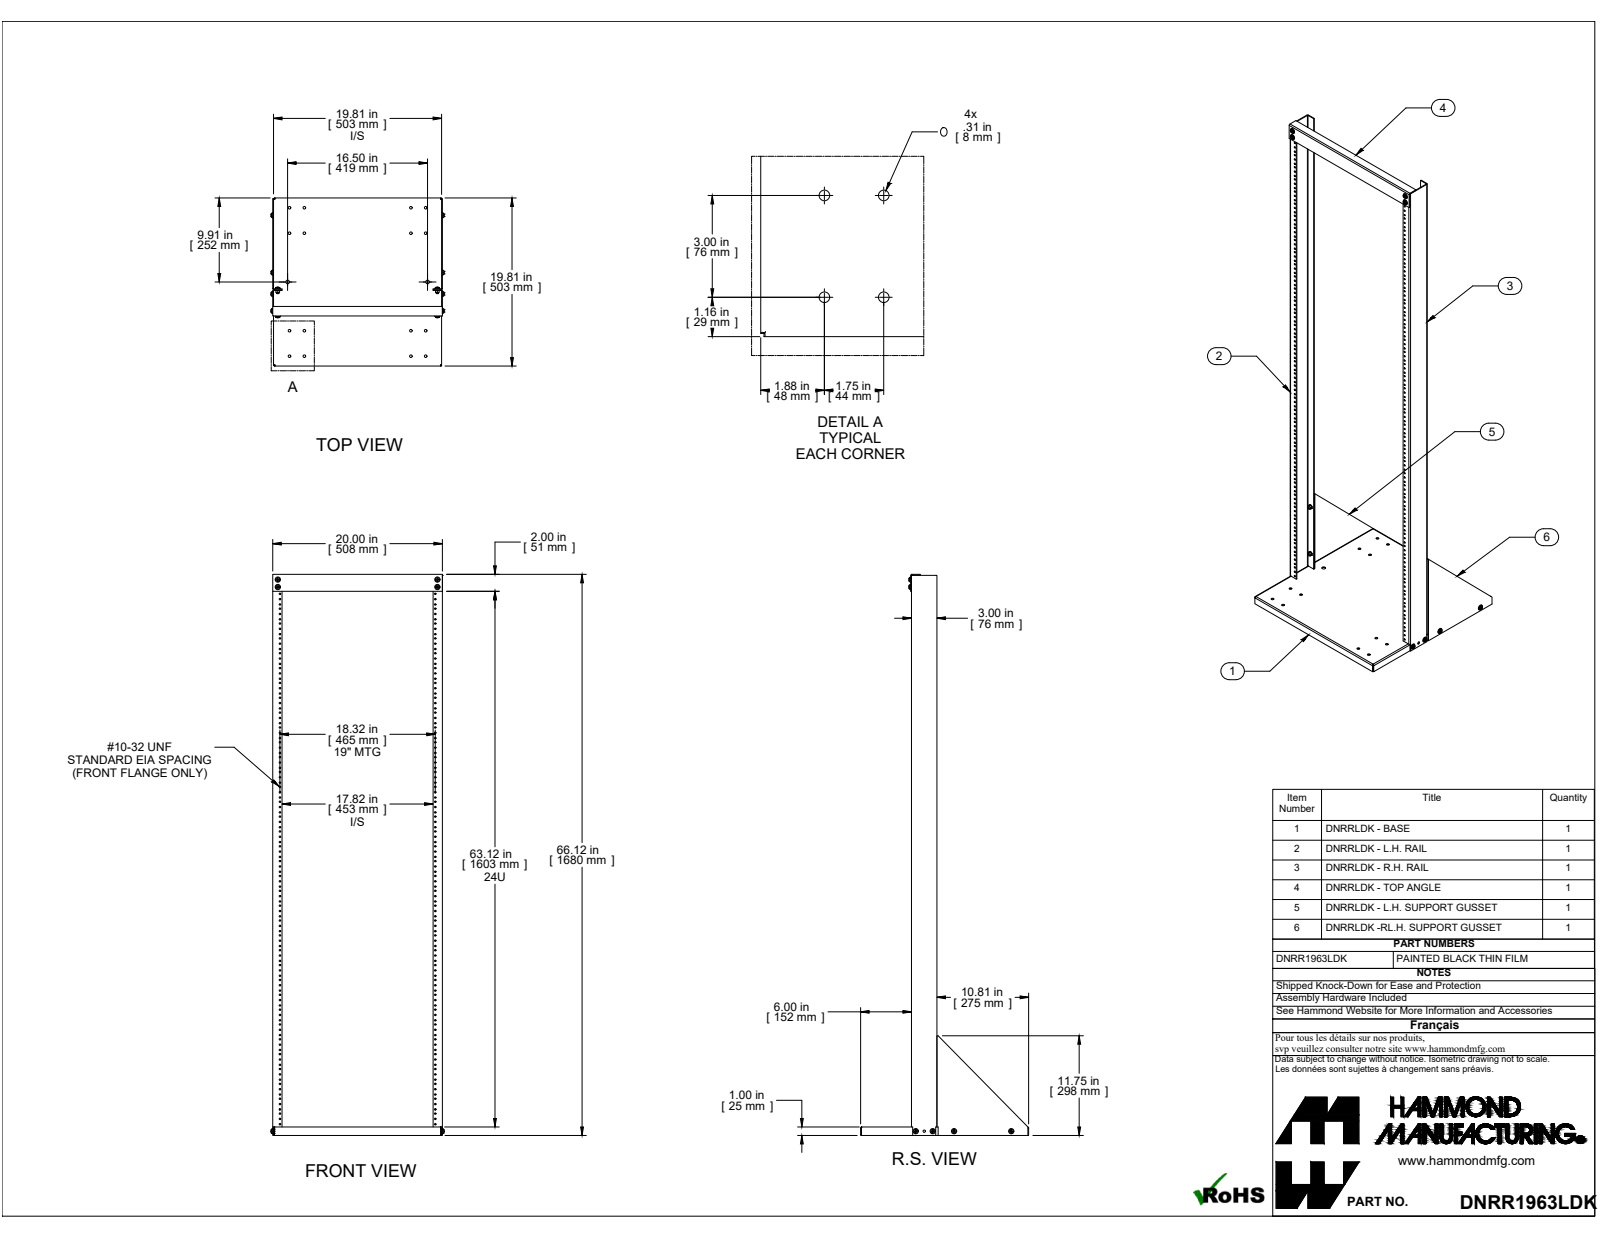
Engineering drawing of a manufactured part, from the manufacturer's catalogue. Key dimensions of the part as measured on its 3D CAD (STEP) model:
Part name (STEP PRODUCT): DNRR1963LDK
STEP written by: SolidWorks 2019 (CONFIG_CONTROL_DESIGN)
Units: inches
Bodies: 54 solids, 1062 faces (584 planar, 374 cylindrical, 104 other)
Overall size (bounding box): 66.125 × 20.398 × 19.812
Volume: 126.1 in³ · Surface area: 2 729 in²
Round holes (diameter × count): ⌀0.177 ×216, ⌀0.313 ×18, ⌀0.281 ×15, ⌀0.196 ×12, ⌀0.282 ×12, ⌀0.437 ×2
Round bosses / shafts (diameter × count): ⌀0.468 ×12, ⌀0.25 ×12, ⌀0.625 ×6, ⌀0.625 ×6
Partial cylindrical surfaces — rounded edges, fillets, slot ends (radius × count): R0.048 ×11, R0.143 ×11, R0.156 ×4
Main face-to-face distances: 0.095, 0.095, 19.907, 19.812, 20.002, 3, 2.905, 2.81, 2.905, 0.19
Hole centre spacings: 1.75, 3.5, 5.25, 3, 7, 8.75, 10.5, 0.625
